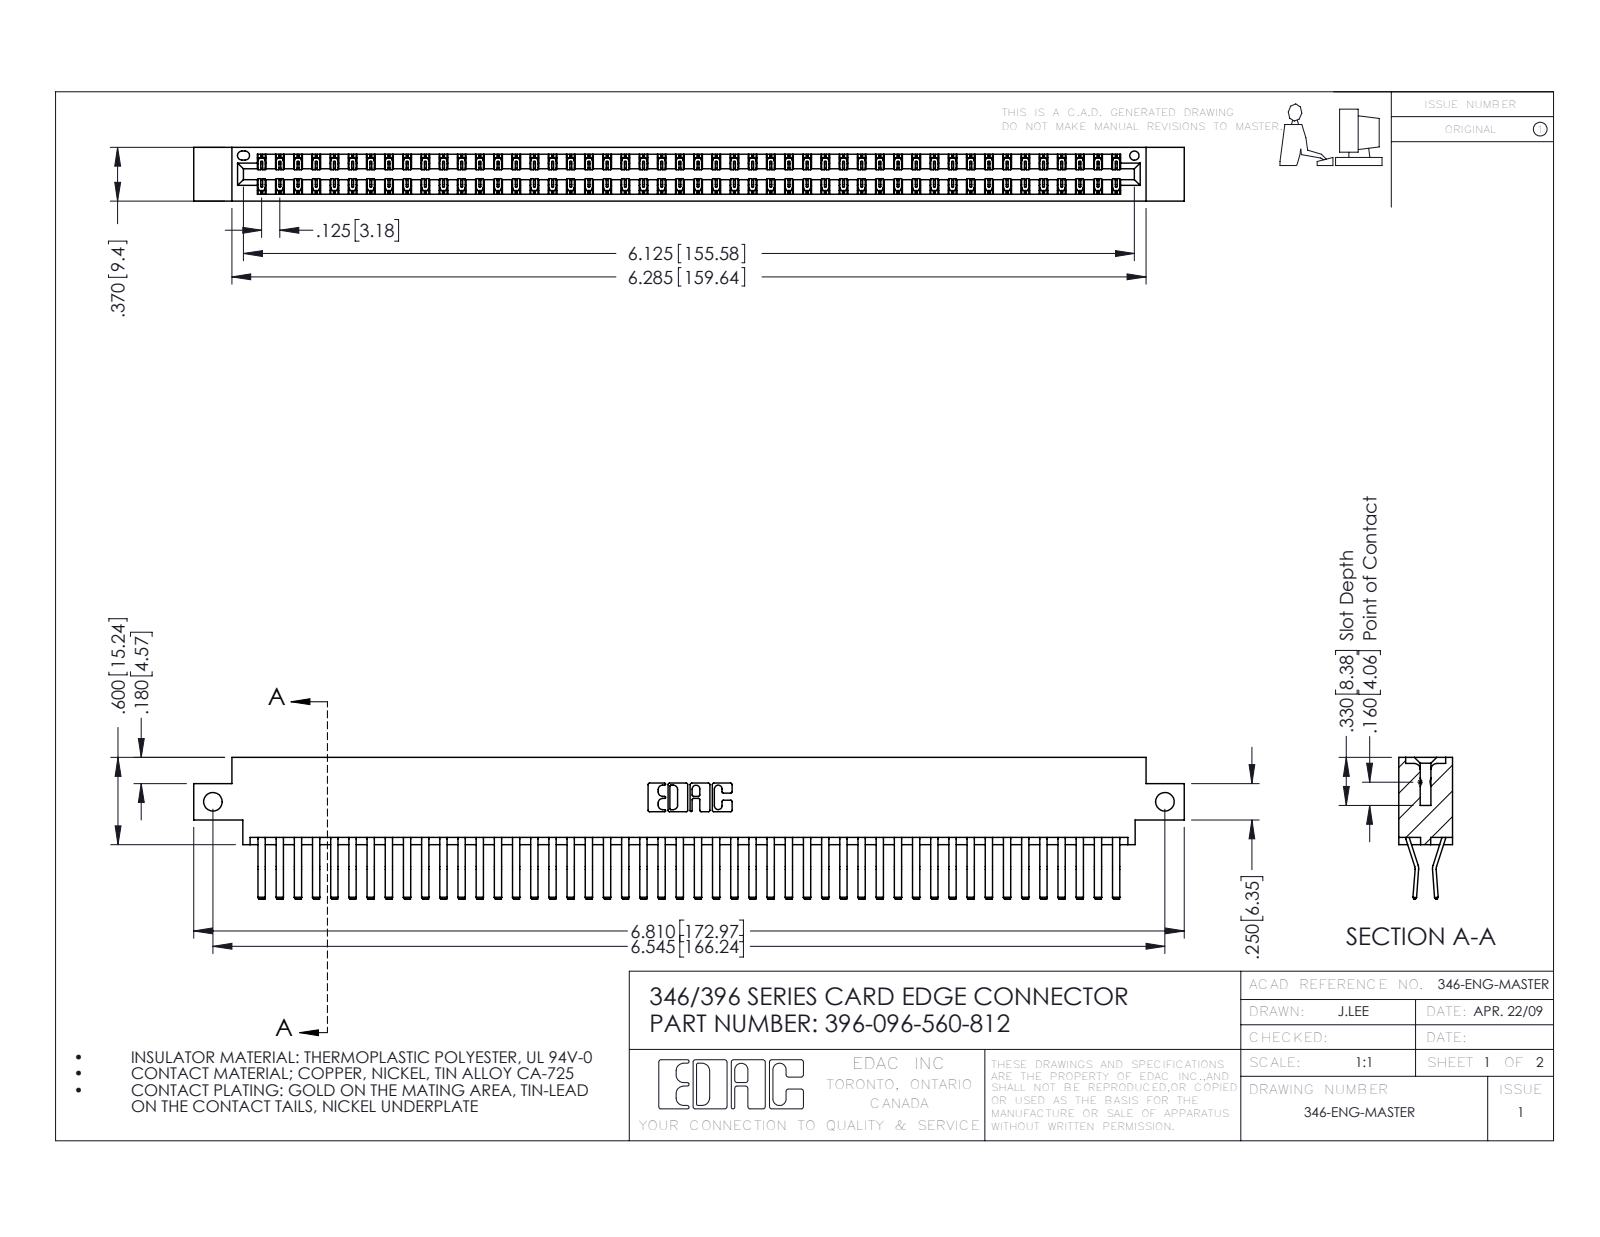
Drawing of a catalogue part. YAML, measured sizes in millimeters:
part_name: "346 Part_0.170 Offset - Side Mount; 345-292-001_560 Tail; 396-096-560-812"
step_written_by: "SolidWorks 2016 (CONFIG_CONTROL_DESIGN)"
units: millimeters
bodies: {solids: 97, faces: 5310, planar: 3440, cylindrical: 1870, other: 0}
overall_size: [173, 24.8, 9.4]
volume: 17300
surface_area: 25600
round_holes:
  - {diameter: 3.3, count: 2}
  - {diameter: 1.6, count: 1}
partial_cylinders:
  - {radius: 0.2, count: 144}
  - {radius: 0.3, count: 22}
  - {radius: 0.2, count: 6}
  - {radius: 0.8, count: 6}
  - {radius: 0.7, count: 3}
  - {radius: 0.3, count: 2}
  - {radius: 0.4, count: 2}
  - {radius: 0.6, count: 2}
face_to_face_distances: [1.2, 8.2, 9.4, 0.6, 6.4, 1.8, 7.6, 7, 3.8, 5.6]
hole_center_spacings: [166.2]
